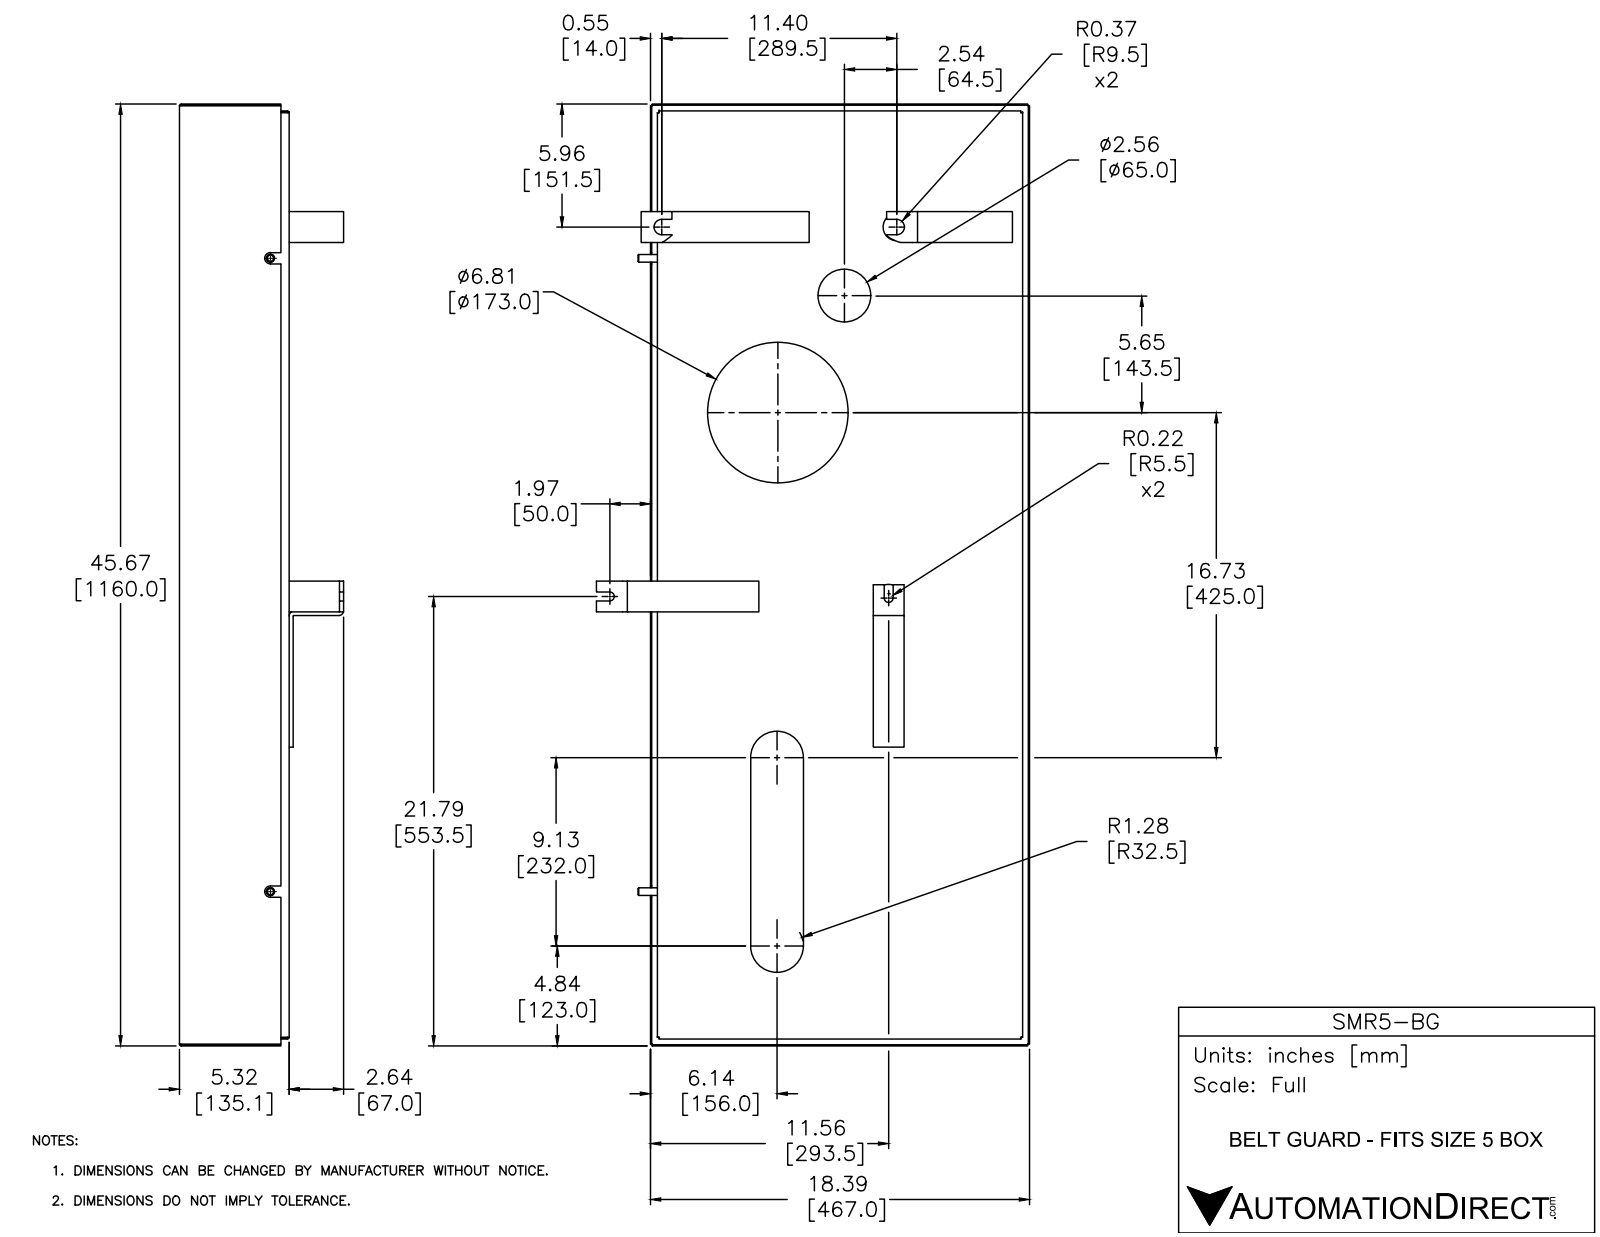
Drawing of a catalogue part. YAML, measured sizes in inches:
part_name: "SMR5-BG"
step_written_by: "SolidWorks 2016 (AUTOMOTIVE_DESIGN)"
units: inches
bodies: {solids: 8, faces: 202, planar: 122, cylindrical: 60, other: 20}
overall_size: [45.669, 21.004, 7.958]
volume: 150.2
surface_area: 4845
round_holes:
  - {diameter: 0.394, count: 2}
  - {diameter: 1.319, count: 2}
  - {diameter: 2.559, count: 1}
  - {diameter: 6.811, count: 1}
round_bosses_or_shafts:
  - {diameter: 0.374, count: 2}
partial_cylinders:
  - {radius: 0.029, count: 16}
  - {radius: 0.088, count: 8}
  - {radius: 0.226, count: 8}
  - {radius: 0.217, count: 2}
  - {radius: 0.276, count: 2}
  - {radius: 0.374, count: 2}
  - {radius: 1.28, count: 2}
  - {radius: 1.777, count: 1}
face_to_face_distances: [0.059, 5.261, 5.32, 5.202, 18.327, 0.335, 17.992, 18.268, 18.386, 45.61]
hole_center_spacings: [4.185, 6.524, 10.479, 10.686, 14.822, 17.996, 30.709]
